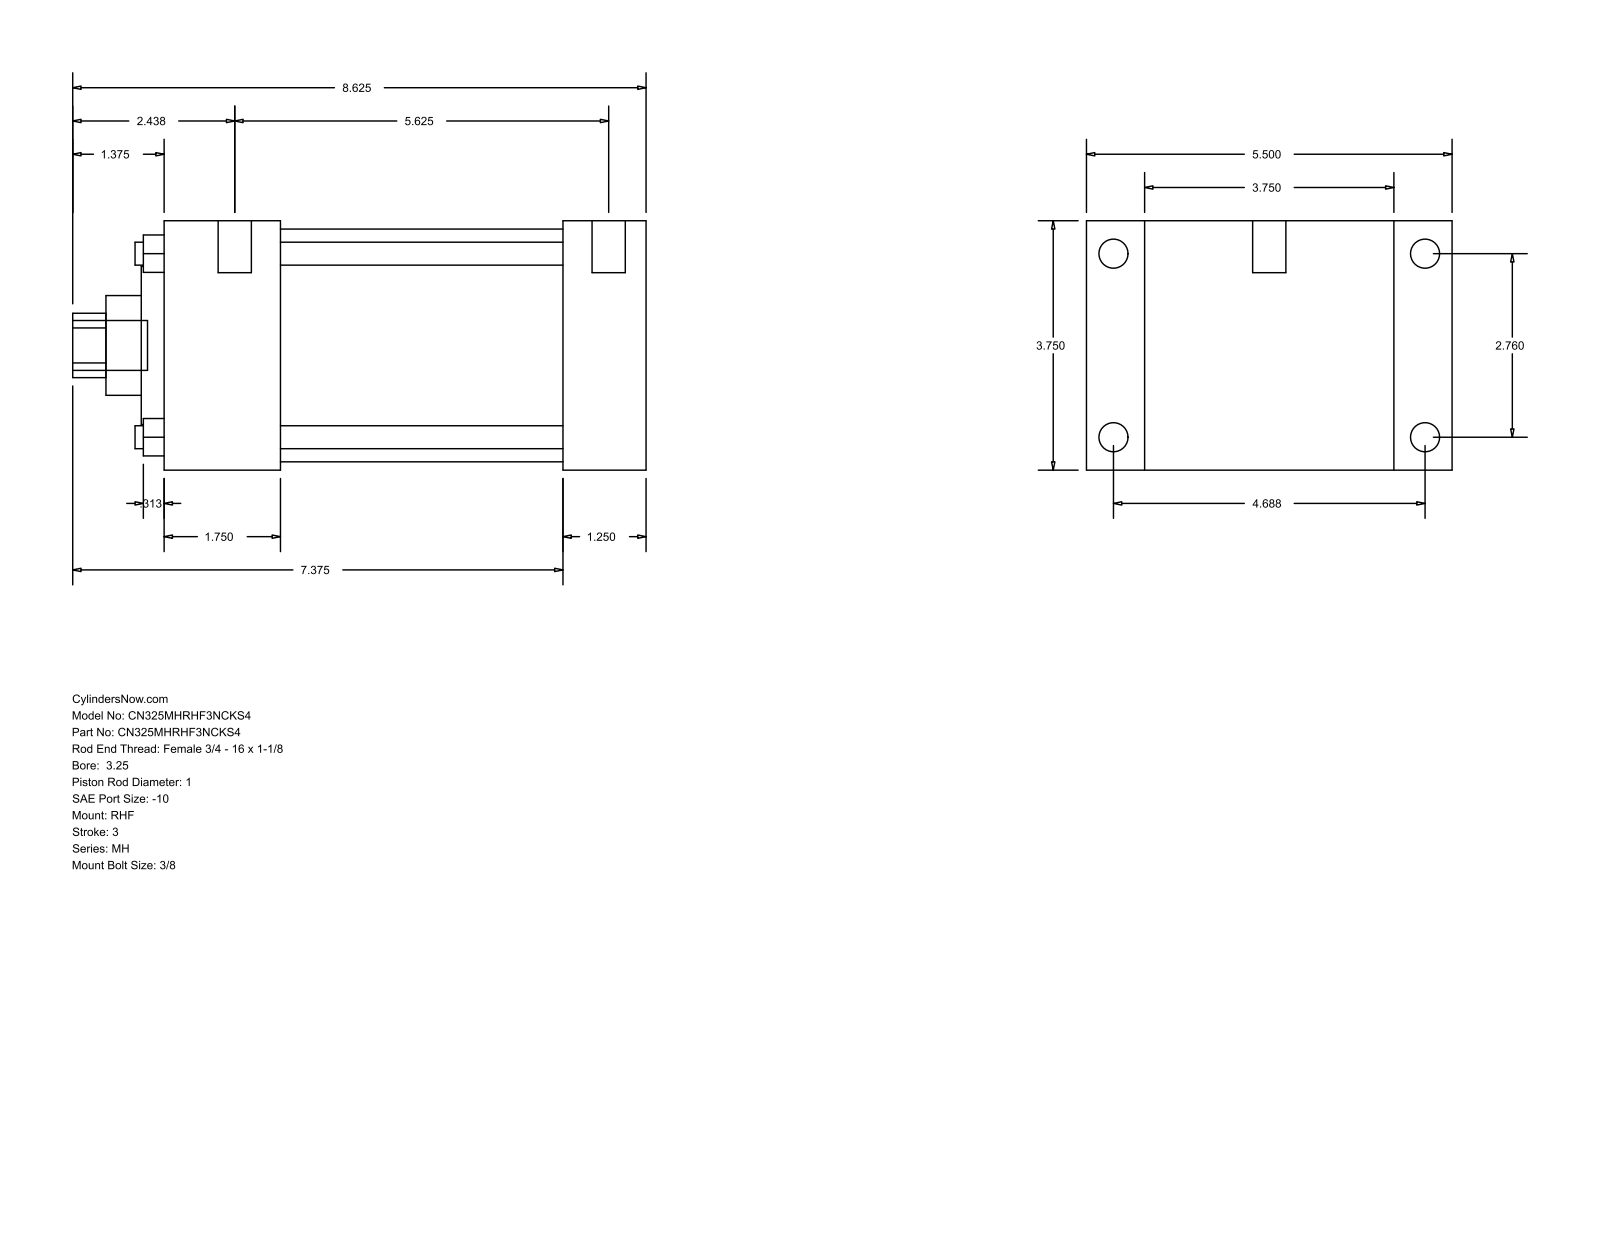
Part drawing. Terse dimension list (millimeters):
name: MH_RHF__0325_1
written by: GSSL Pune (CONFIG_CONTROL_DESIGN)
unit: mm
bodies: 0 solids, 90 faces (61 planar, 29 cylindrical, 0 other)
size: 219.07 × 139.7 × 95.25
holes: 4× ⌀8.76, 1× ⌀25.4, 1× ⌀38.1, 1× ⌀60.33, 1× ⌀88.9
bosses: 4× ⌀11.13, 4× ⌀5.56, 2× ⌀12.7, 1× ⌀19.05
rounds: 1× R12.29
face distances: 95.24, 31.75, 22.23, 117.47, 152.4, 184.15, 139.7, 44.46, 107.94, 139.69
hole spacings: 49.57, 70.1, 99.14
